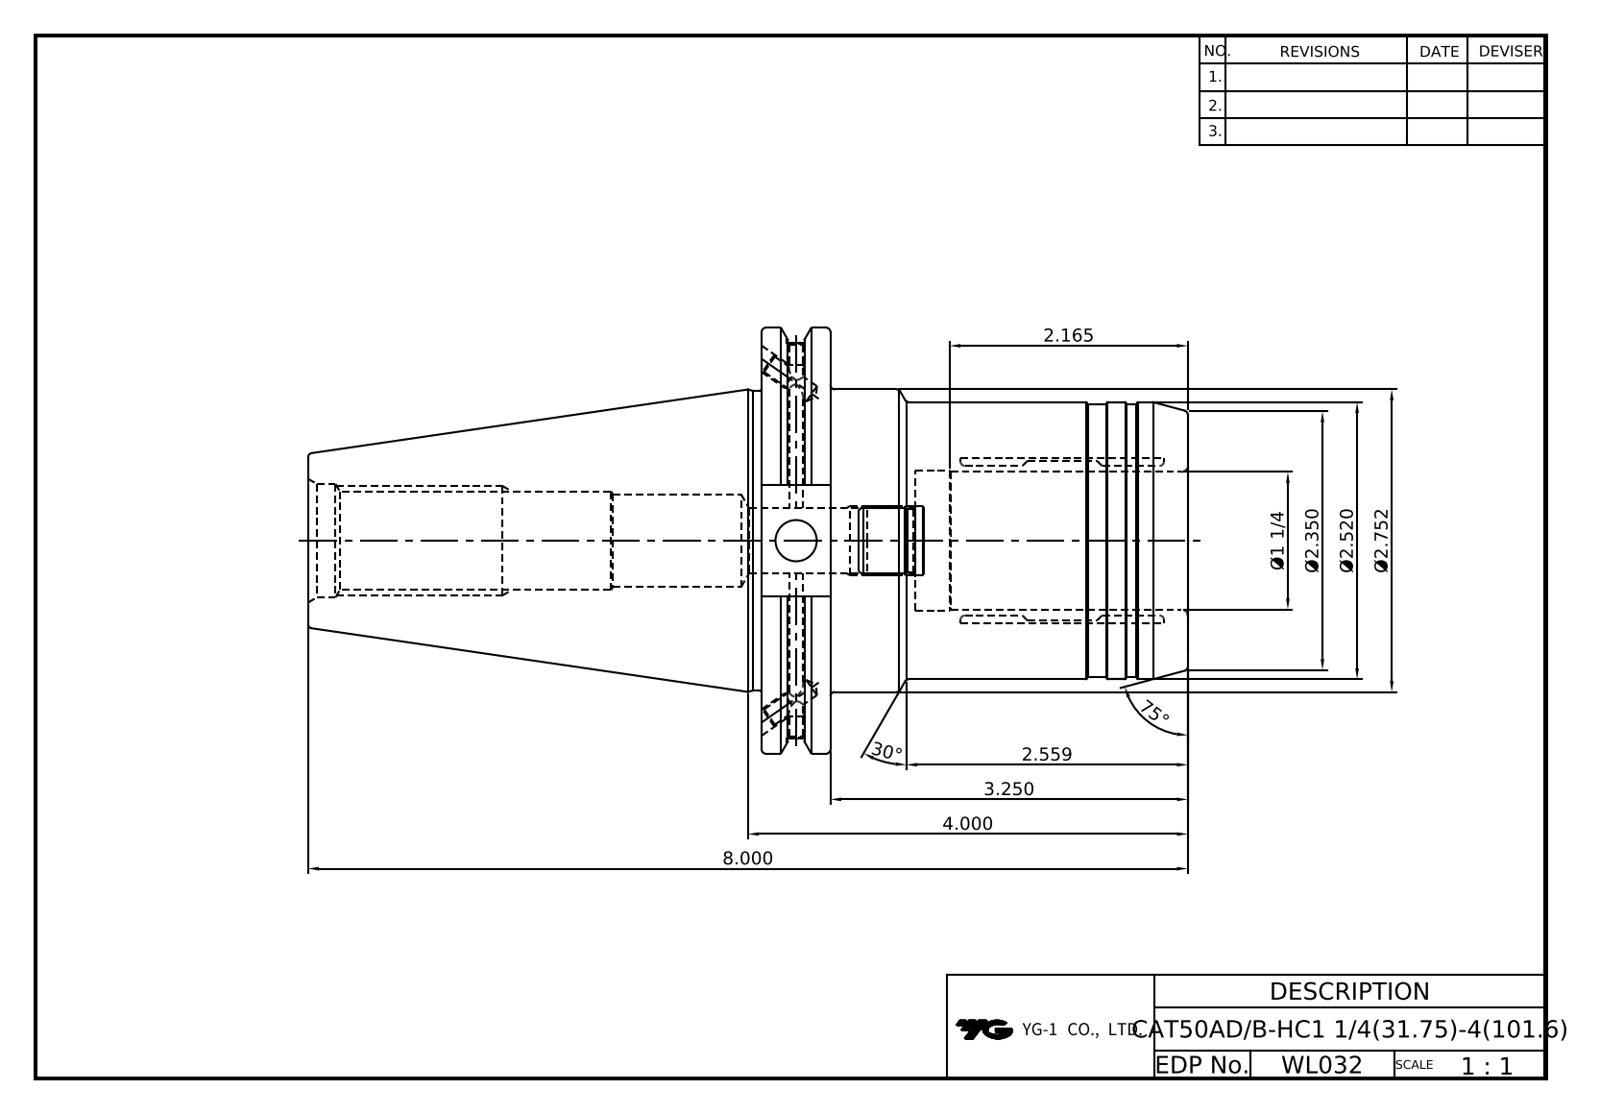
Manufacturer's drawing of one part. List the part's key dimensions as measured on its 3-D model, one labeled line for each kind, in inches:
Part name (STEP PRODUCT): LO-CAT50ADB-HC31.75-101.6
STEP written by: Autodesk Inventor 2022 (AUTOMOTIVE_DESIGN)
Units: inches
Bodies: 1 solid, 106 faces (37 planar, 32 cylindrical, 37 other)
Overall size (bounding box): 8 × 3.875 × 3.728
Volume: 33.17 in³ · Surface area: 105.4 in²
Round holes (diameter × count): ⌀0.128 ×2, ⌀0.163 ×2, ⌀0.165 ×2, ⌀0.197 ×2, ⌀0.375 ×1, ⌀0.587 ×1, ⌀0.807 ×1, ⌀0.865 ×1, ⌀1.031 ×1, ⌀1.25 ×1, ⌀1.283 ×1
Round bosses / shafts (diameter × count): ⌀3.875 ×1, ⌀3.594 ×1, ⌀2.752 ×1, ⌀2.726 ×1, ⌀2.52 ×1, ⌀2.48 ×1
Main face-to-face distances: 0.625, 3.875, 3.25, 1.395, 0.77, 2.48, 4.125, 4.75, 5.52, 8
